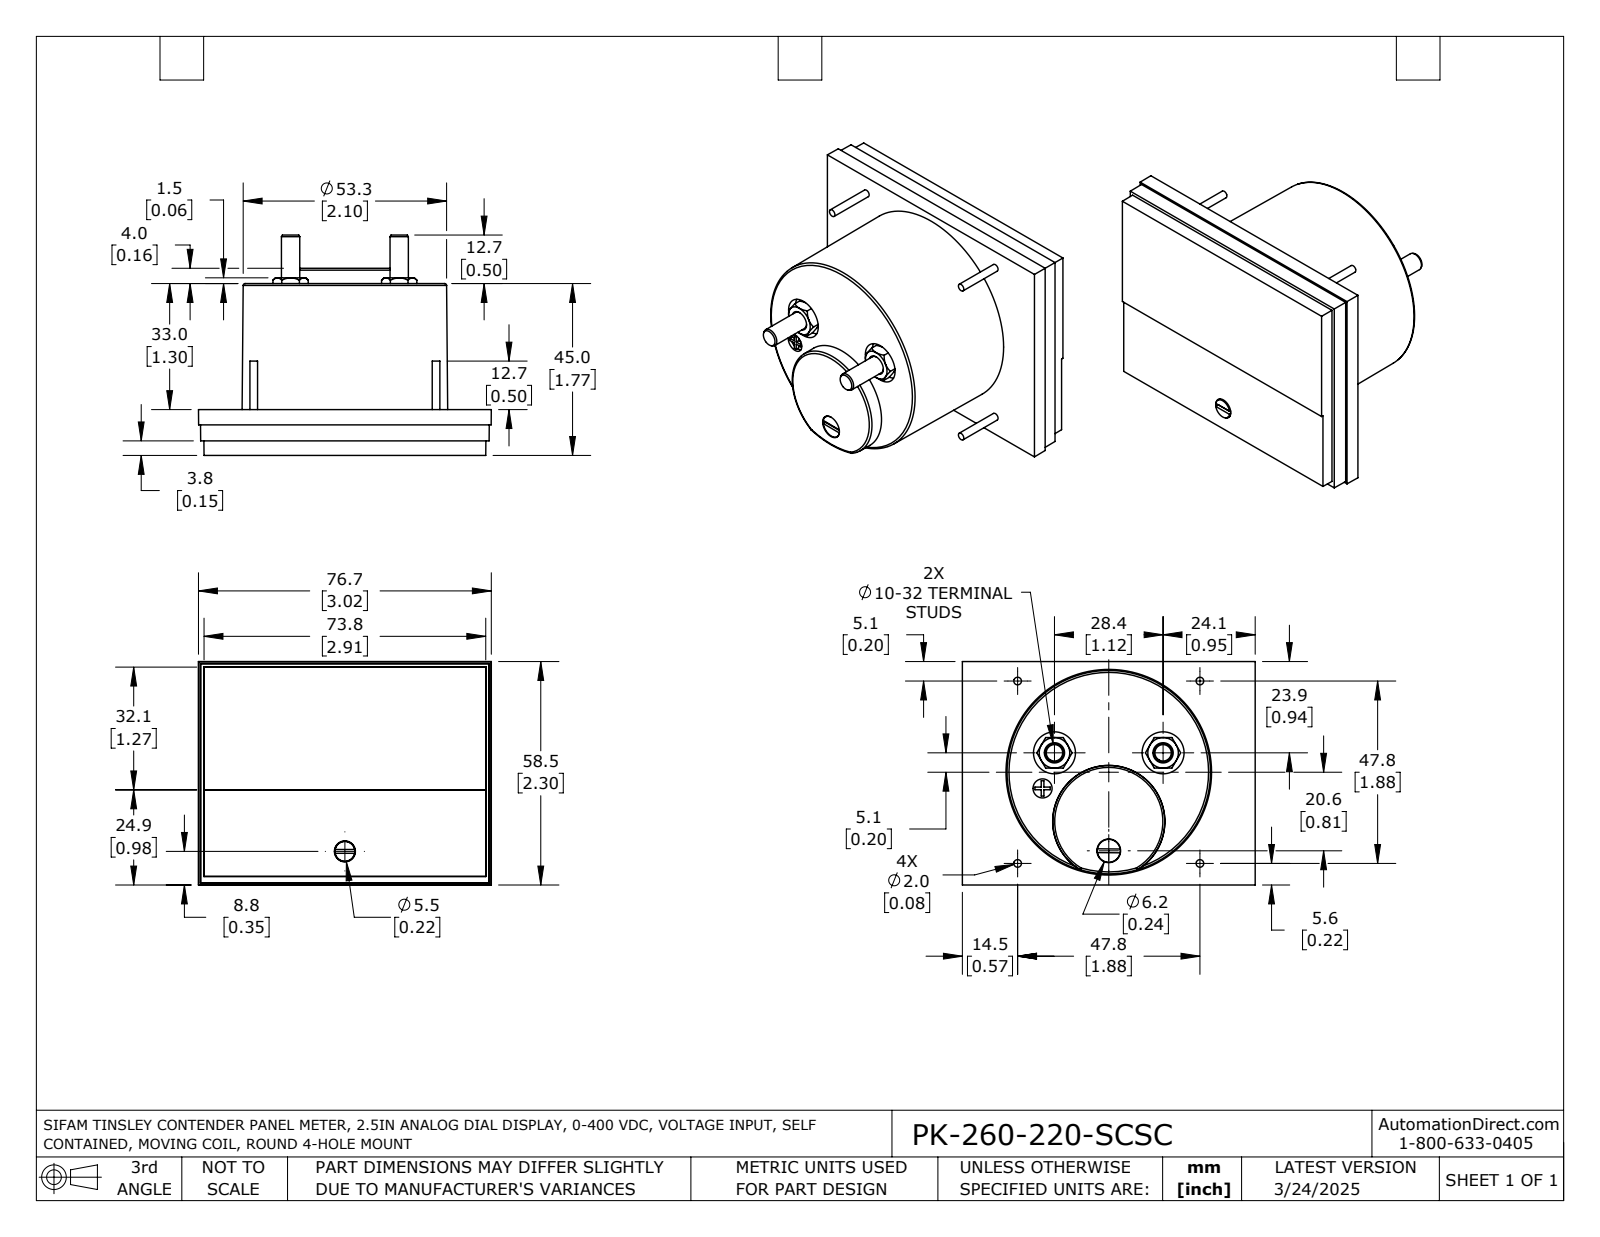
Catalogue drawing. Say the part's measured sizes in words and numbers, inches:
The part is named "PK-260-220-SCSC". Its 3-D file was written by "SolidWorks 2021 (AUTOMOTIVE_DESIGN)". It is 1 solid with 192 faces: 95 planar, 37 cylindrical and 60 other. Overall it measures 3.02 by 2.303 by 2.272 inches. Its volume is 7.657 cubic inches and its surface area 36.55 square inches. Round holes: 3 of diameter 0.197, 2 of diameter 0.433, 1 of diameter 0.209, 1 of diameter 0.217, 1 of diameter 0.244. Round bosses or shafts: 4 of diameter 0.079, 2 of diameter 0.189, 1 of diameter 0.236, 1 of diameter 0.205. Partial cylindrical surfaces (rounded edges, fillets, slot ends): 1 of radius 0.033. The main face-to-face distances are 0.02, 0.472, 0.13, 0.322, 0.15, 0.453, 0.057, 0.077, 0.396, 0.073. The hole center spacings are 1.155, 1.16, 0.387, 0.938, 0.942, 1.12, 1.295.
